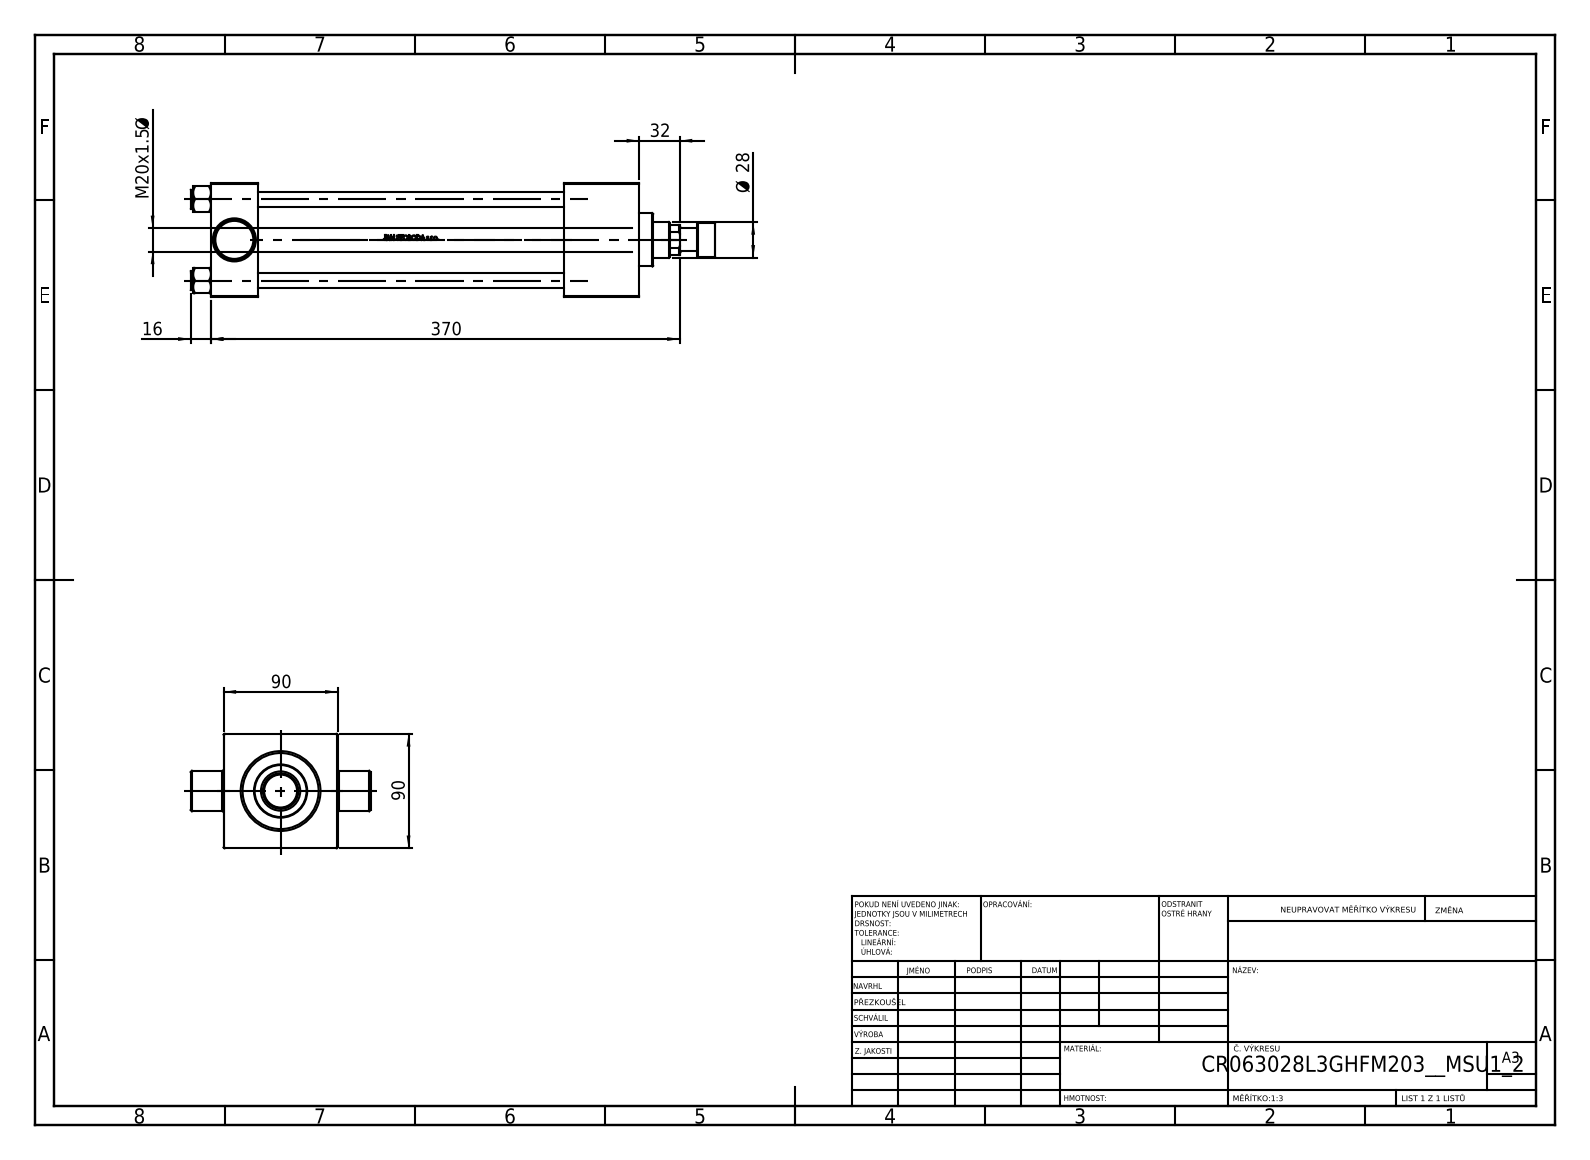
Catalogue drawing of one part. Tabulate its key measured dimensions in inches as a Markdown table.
| quantity | value |
| --- | --- |
| part name | V215CR_ROD_END_F; V215CR_VCP_L; V215CR_L_Body; V215CR_L_TYCINKA (+2 more) |
| STEP written by | SolidWorks 2019 (CONFIG_CONTROL_DESIGN) |
| units | inches |
| bodies | 12 solids, 1071 faces (429 planar, 114 cylindrical, 528 other) |
| overall size | 16.299 × 5.591 × 3.543 |
| volume | 80.8 in³ |
| surface area | 464.3 in² |
| round holes (diameter × count) | 0.472 × 4, 0.276 × 1, 0.728 × 1, 1.102 × 1, 1.22 × 1, 1.969 × 1, 2.362 × 1, 2.48 × 1 |
| round bosses / shafts (diameter × count) | 0.591 × 4, 2.717 × 1, 1.654 × 1, 1.26 × 1, 1.063 × 1, 0.709 × 1 |
| main face-to-face distances | 3.543, 1.457, 13.307, 11.85, 3.504, 2.323, 0.02, 9.528, 10.984, 3.524 |
| hole center spacings | 1.79, 2.531, 3.58 |
